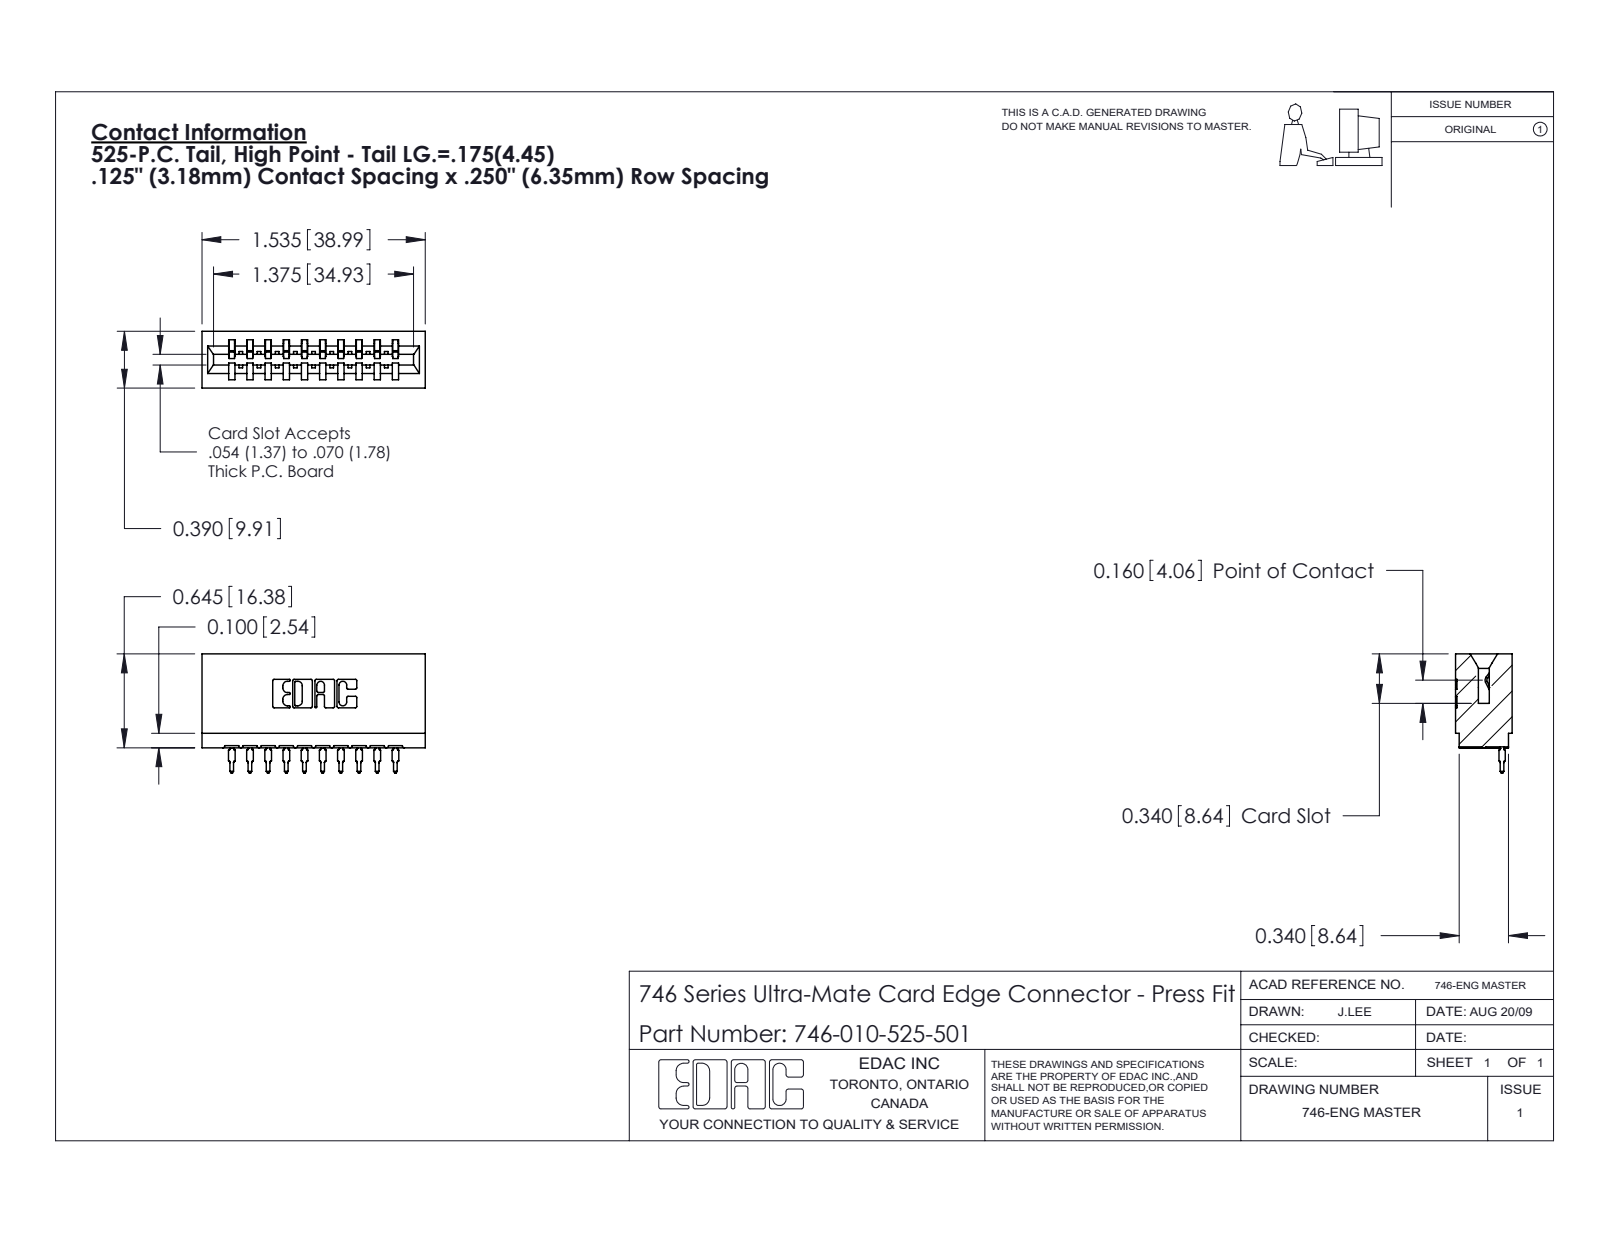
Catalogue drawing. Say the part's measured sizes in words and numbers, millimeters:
The part is named "746 Part_.340 Slot Depth - 01; 746-010-525-501; 746-292-001_525". Its 3-D file was written by "SolidWorks 2020 (CONFIG_CONTROL_DESIGN)". It is 11 solids with 1177 faces: 685 planar, 232 cylindrical and 260 other. Overall it measures 39 by 20.8 by 9.9 millimeters. Its volume is 4 560 cubic millimeters and its surface area 5 610 square millimeters. Partial cylindrical surfaces (rounded edges, fillets, slot ends): 22 of radius 0.3, 20 of radius 0.5, 11 of radius 0.4, 6 of radius 0.2, 6 of radius 0.8, 4 of radius 0.1, 4 of radius 0.3, 3 of radius 0.7. The main face-to-face distances are 6.4, 12.7, 1.1, 3.2, 8.5, 1.4, 7.4, 9.5, 3.2, 9.9.
